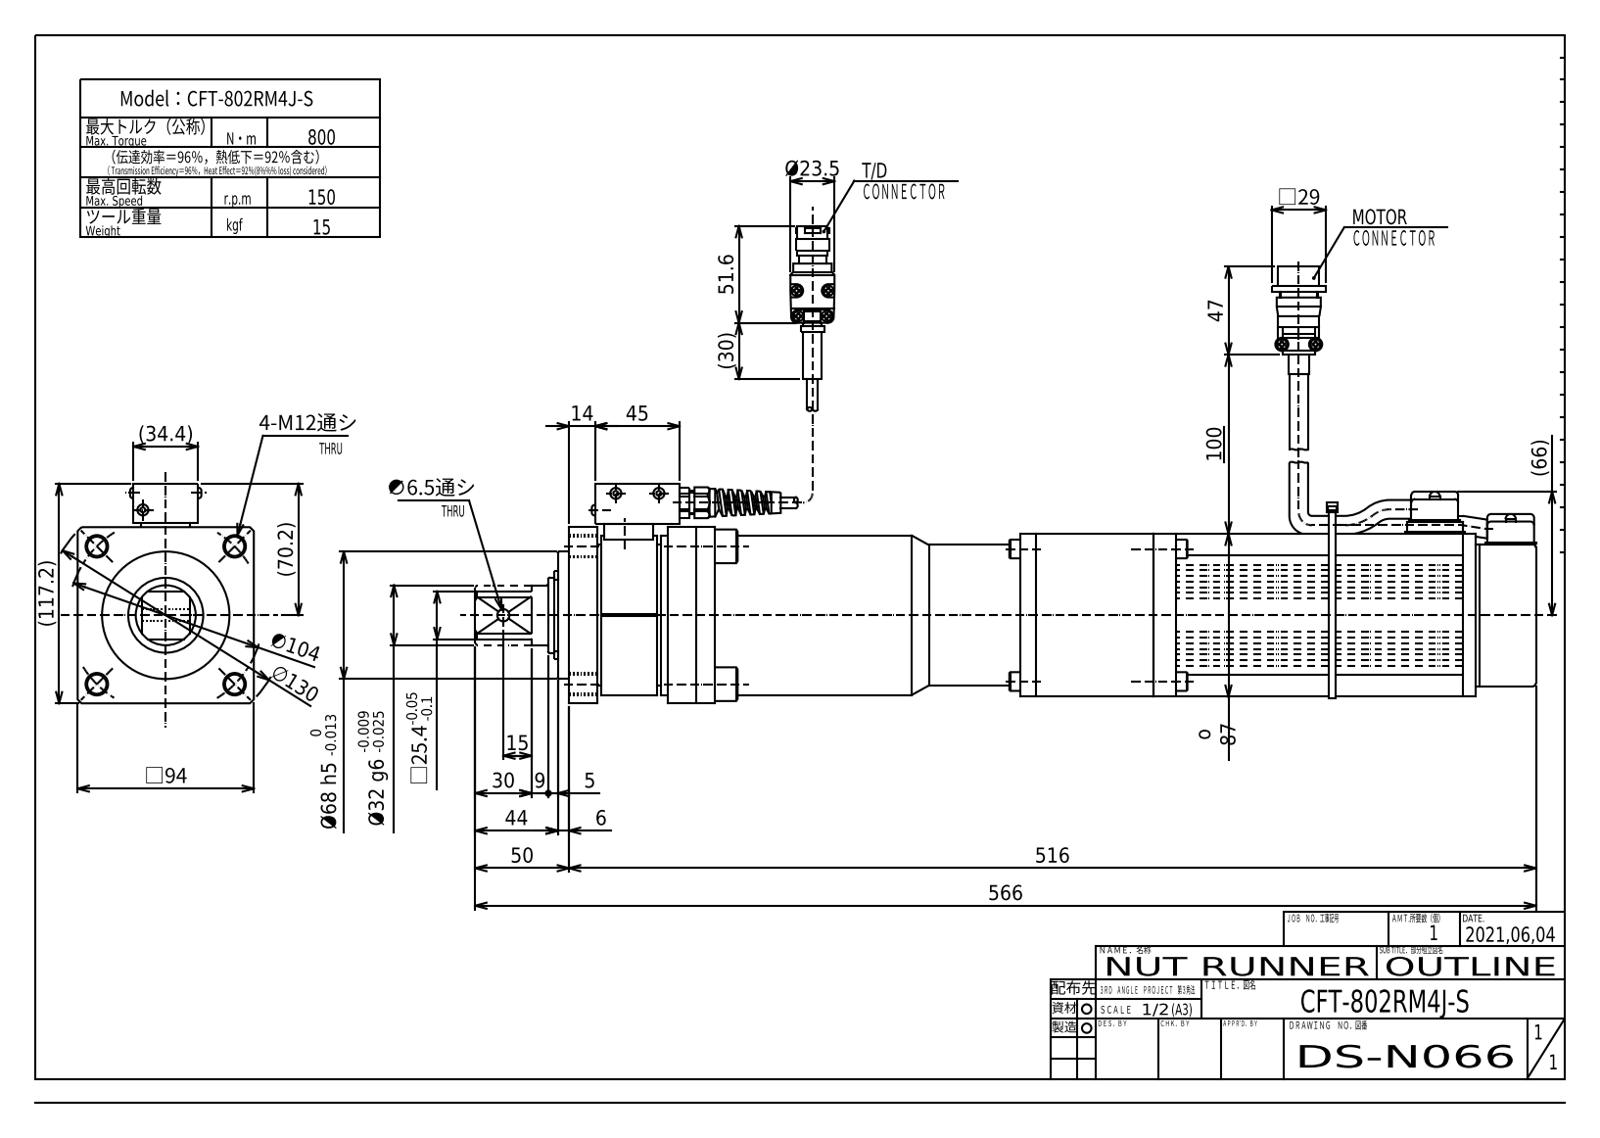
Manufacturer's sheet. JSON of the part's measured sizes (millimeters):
{"part_name": "CFT-802RM4J-S(DS-N066)_OUTLINE_20210803", "step_written_by": "Autodesk Inventor 2021 (AUTOMOTIVE_DESIGN)", "units": "millimeters", "bodies": {"solids": 1, "faces": 1117, "planar": 663, "cylindrical": 262, "other": 192}, "overall_size": [566, 117.2, 94], "volume_mm3": 3347000, "surface_area_mm2": 278084, "round_holes": [[6.5, 5], [10.25, 4], [2.5, 2], [61.53, 1]], "round_bosses_or_shafts": [[8, 7], [7, 5], [18, 4], [10, 4], [8.5, 4], [7.5, 4], [5.7, 3], [3, 2]], "partial_cylinders_radius": [[0.6, 48], [1, 28], [0.5, 13], [3, 8], [1.5, 7], [5, 6], [0.3, 4], [2, 4]], "face_to_face_distances": [3, 1.5, 4.5, 6, 87, 45, 46.5, 42, 43.5, 7.5], "hole_center_spacings": [52, 73.54, 22.3, 37.25, 41.9, 68.17, 70.82, 104]}
